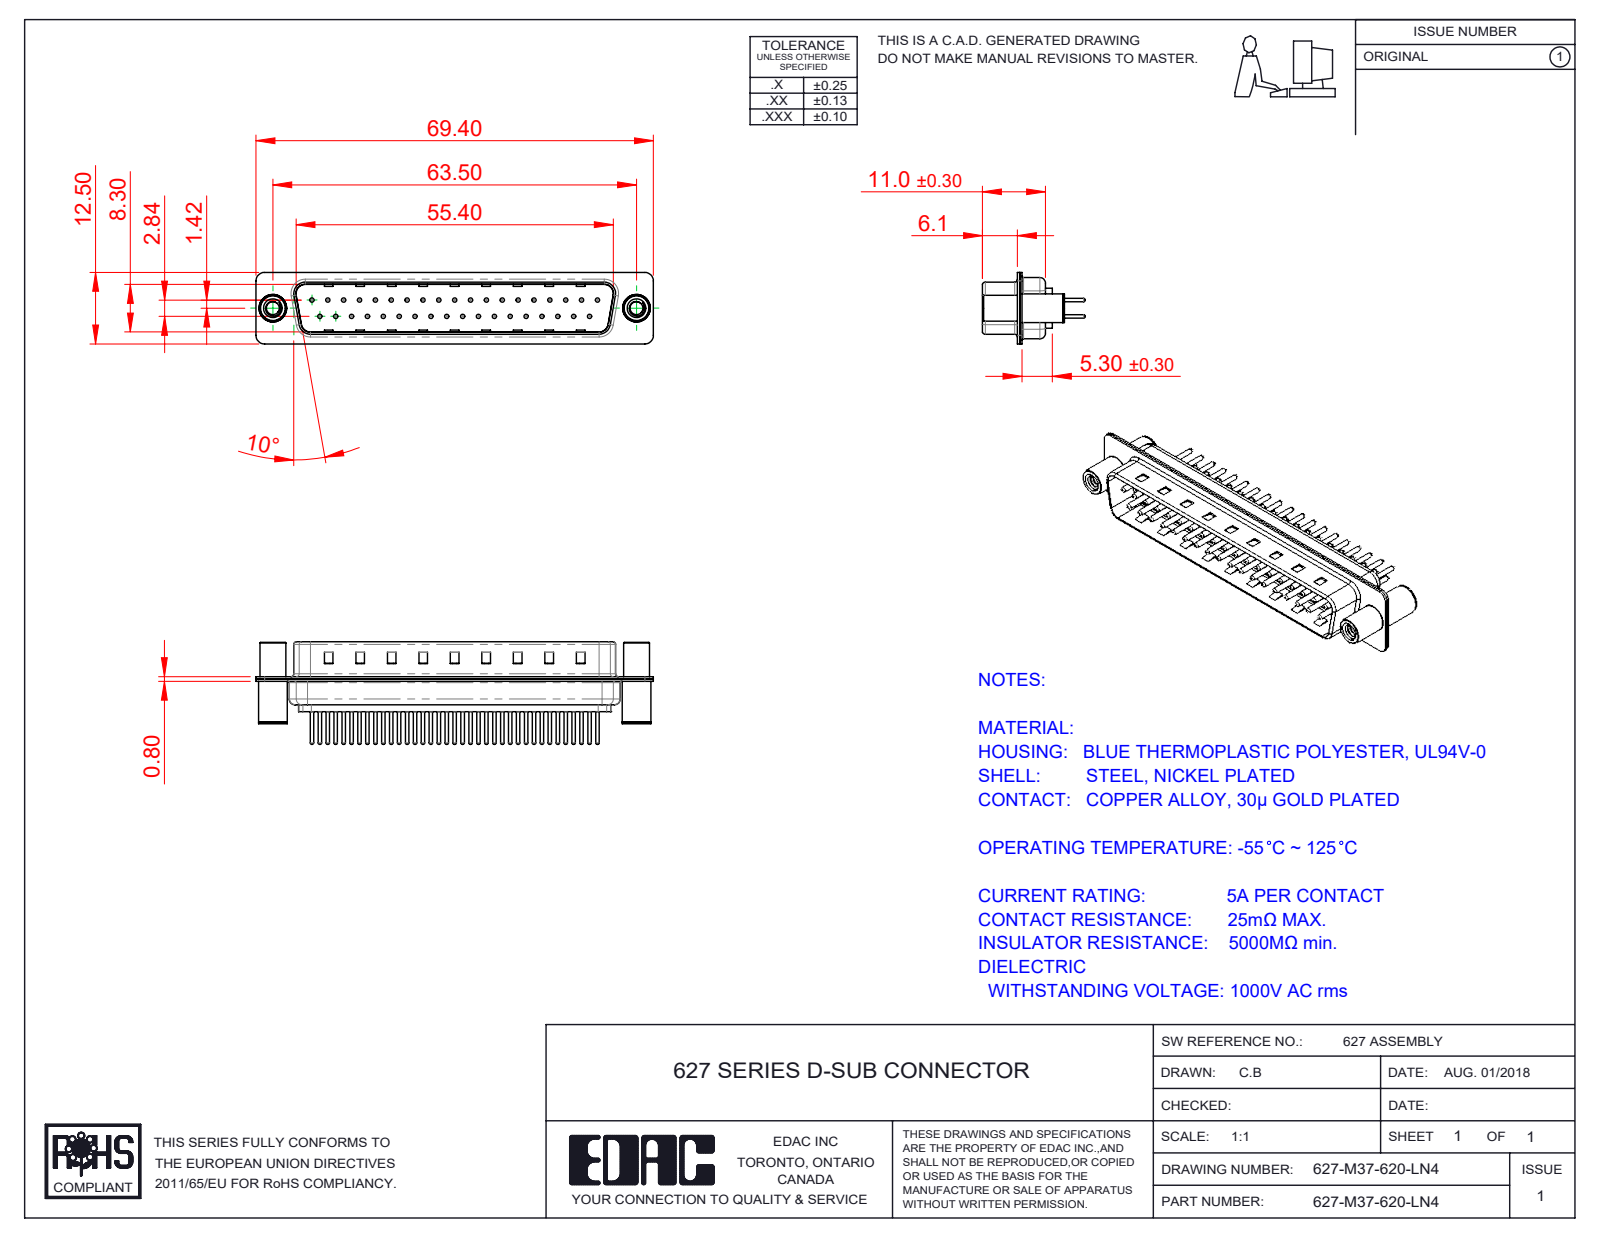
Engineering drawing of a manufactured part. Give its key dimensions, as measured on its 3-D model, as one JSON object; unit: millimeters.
{"part_name": "627-M37-620-LN4; 627M Housing_37 Contacts; 627M Shell Front_37 Contacts; 627M 4-40 Threaded Standoff and Board Spacer (+3 more)", "step_written_by": "SolidWorks 2020 (CONFIG_CONTROL_DESIGN)", "units": "millimeters", "bodies": {"solids": 42, "faces": 1867, "planar": 468, "cylindrical": 711, "other": 688}, "overall_size": [69.4, 17.9, 12.5], "volume_mm3": 4055, "surface_area_mm2": 9799, "round_holes": [[0.75, 37], [1.6, 37], [2, 37], [2.26, 2], [3.26, 2], [4, 2], [4.8, 2]], "round_bosses_or_shafts": [[1.5, 37], [0.6, 37], [5, 2], [4.9, 2], [4.5, 2]], "partial_cylinders_radius": [[1.5, 16], [2, 12], [0.5, 8], [1.6, 8], [0.25, 4], [0.6, 4], [0.65, 4], [0.9, 4]], "face_to_face_distances": [0.4, 0.8, 9.5, 9.1, 8.7, 9.9, 1.2, 5.7, 0.75, 0.35], "hole_center_spacings": [2.77, 5.54, 3.16, 8.31, 11.08, 13.85, 16.62, 19.39]}
